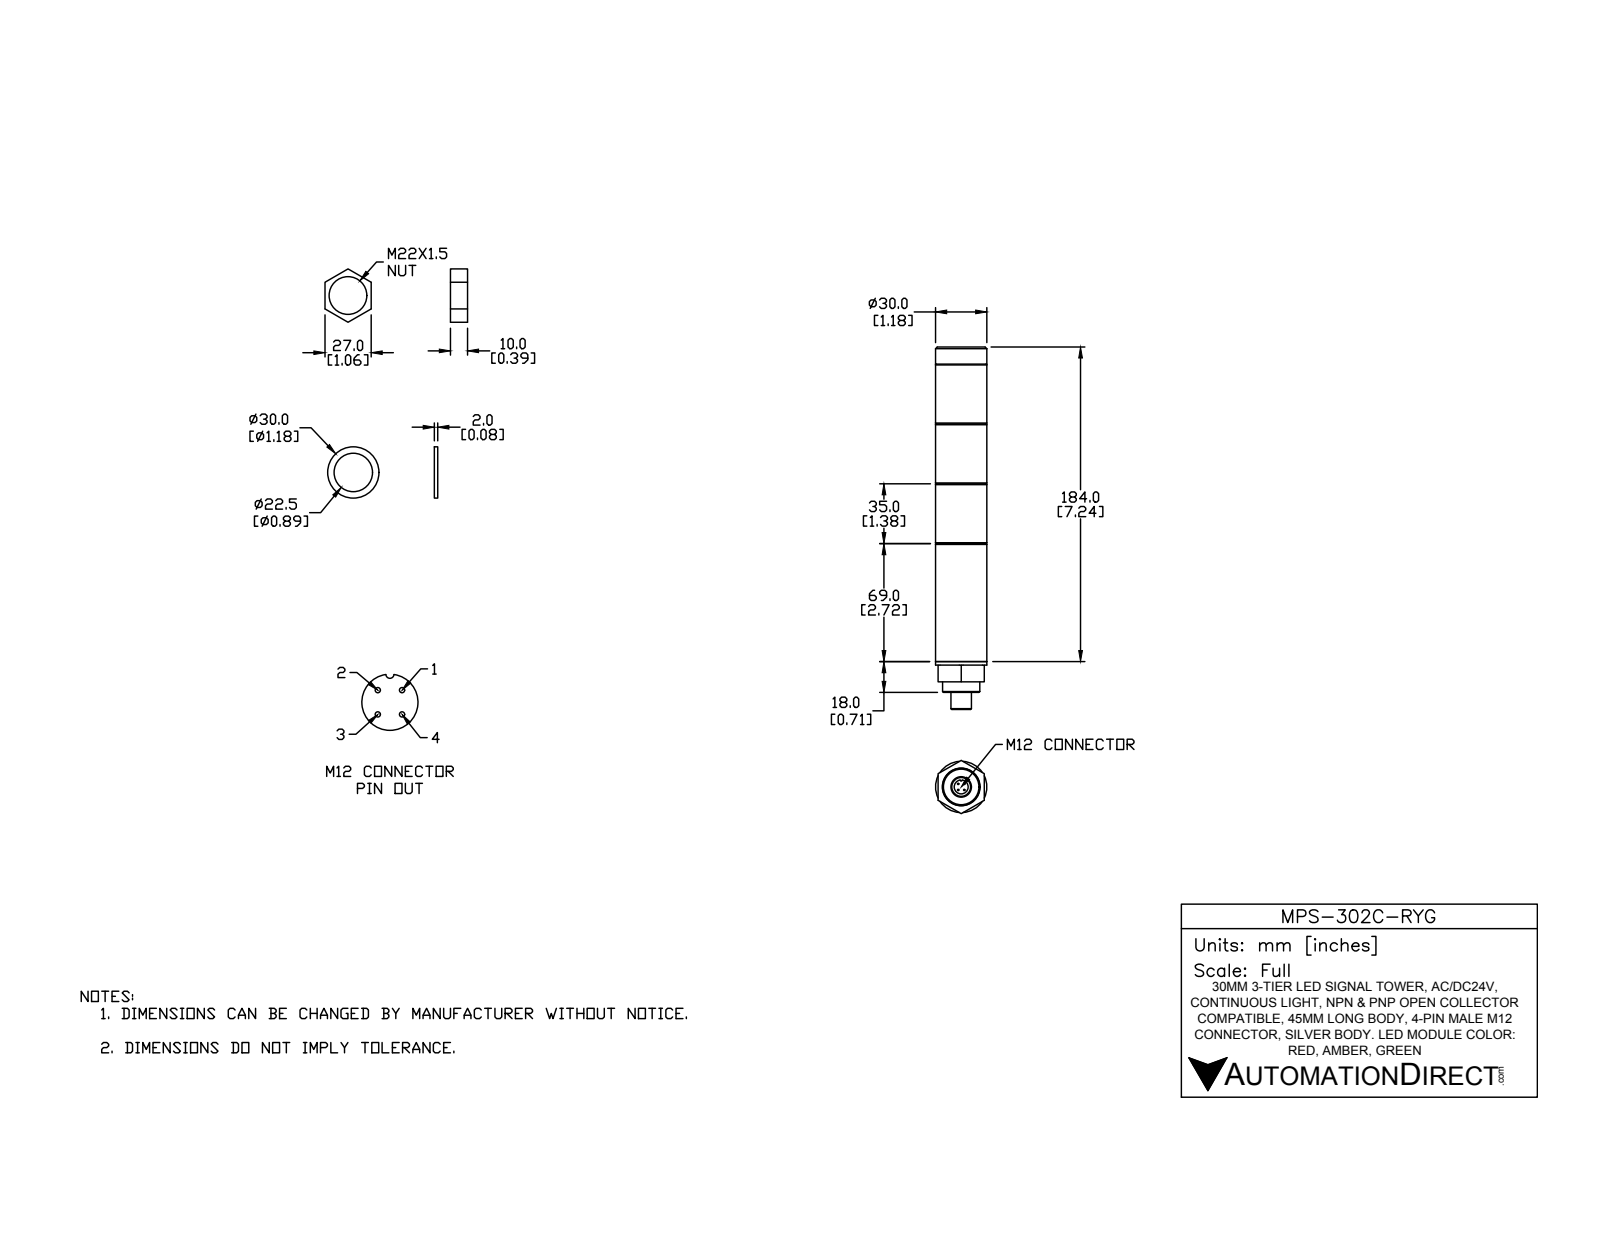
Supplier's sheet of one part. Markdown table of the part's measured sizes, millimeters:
| quantity | value |
| --- | --- |
| part name | MPS-302C-RYG |
| STEP written by | SolidWorks 2016 (AUTOMOTIVE_DESIGN) |
| units | millimeters |
| bodies | 12 solids, 114 faces (45 planar, 39 cylindrical, 30 other) |
| overall size | 212 × 31.18 × 30 |
| volume | 129 197 mm³ |
| surface area | 32 173 mm² |
| round holes (diameter × count) | 3.2 × 1, 7.7 × 1, 8.2 × 1, 20.7 × 1, 22 × 1 |
| round bosses / shafts (diameter × count) | 0.75 × 4, 30 × 1, 21.8 × 1, 12 × 1, 5 × 1 |
| partial cylindrical surfaces (radius × count) | 0.6 × 1 |
| main face-to-face distances | 35, 70, 105, 69, 104, 139, 174, 71, 106, 141 |
